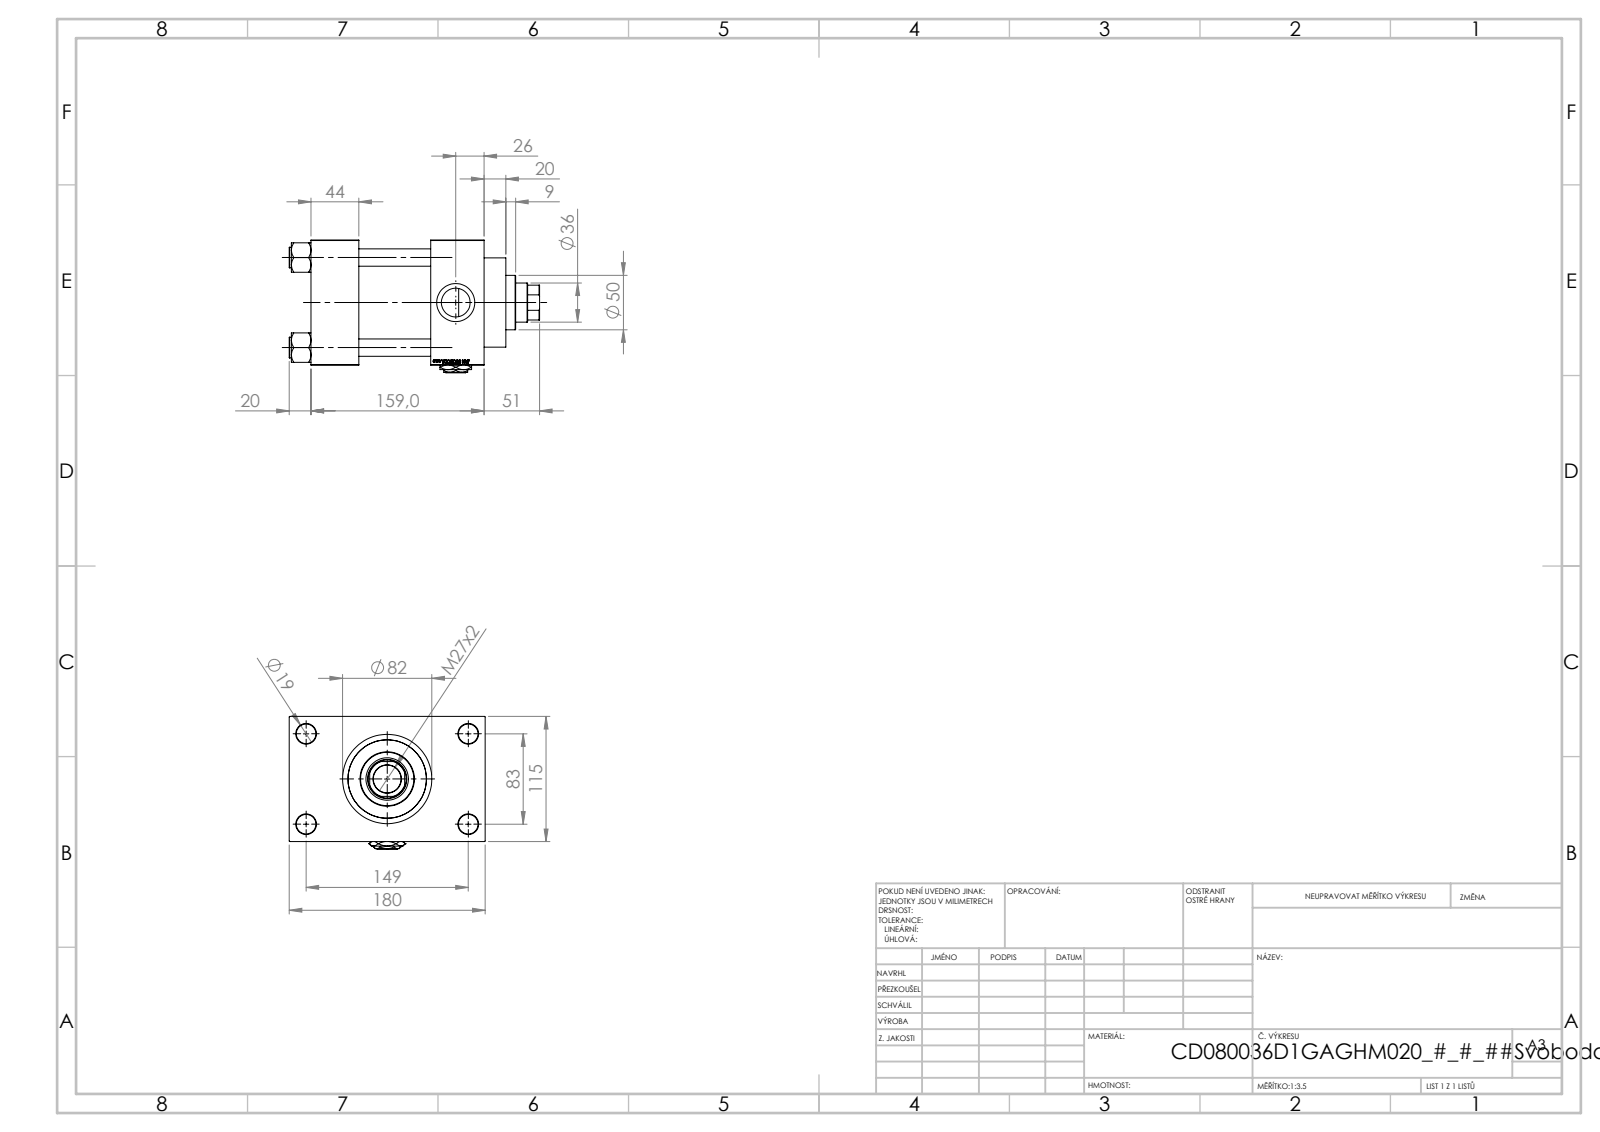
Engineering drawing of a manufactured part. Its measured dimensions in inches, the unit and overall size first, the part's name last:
Units: inches
Overall size (bounding box): 9.055 × 7.087 × 4.803
Round holes (diameter × count): ⌀0.63 ×4, ⌀0.709 ×4, ⌀1.041 ×3, ⌀1.378 ×3, ⌀0.276 ×2, ⌀1.004 ×1, ⌀1.417 ×1, ⌀1.535 ×1, ⌀2.402 ×1, ⌀2.835 ×1, ⌀3.15 ×1
Round bosses / shafts (diameter × count): ⌀0.748 ×4, ⌀3.386 ×1, ⌀3.228 ×1, ⌀1.969 ×1
Partial cylindrical surfaces — rounded edges, fillets, slot ends (radius × count): R0.689 ×1
Main face-to-face distances: 4.528, 2.598, 4.331, 1.929, 1.732, 6.26, 5.807, 1.28, 0.787, 2.717
Hole centre spacings: 1.305, 2.302, 3.256, 3.357, 3.513, 4.561, 5.607, 3.268
Volume: 120.2 in³ · Surface area: 464.3 in²
Bodies: 12 solids, 1200 faces (569 planar, 93 cylindrical, 538 other)
Part name (STEP PRODUCT): V215CD_D_Body; V215CD_D_TYCINKA; V215CD_NUT_M5_D; V215CD_VC_A (+2 more)
STEP written by: SolidWorks 2019 (CONFIG_CONTROL_DESIGN)
